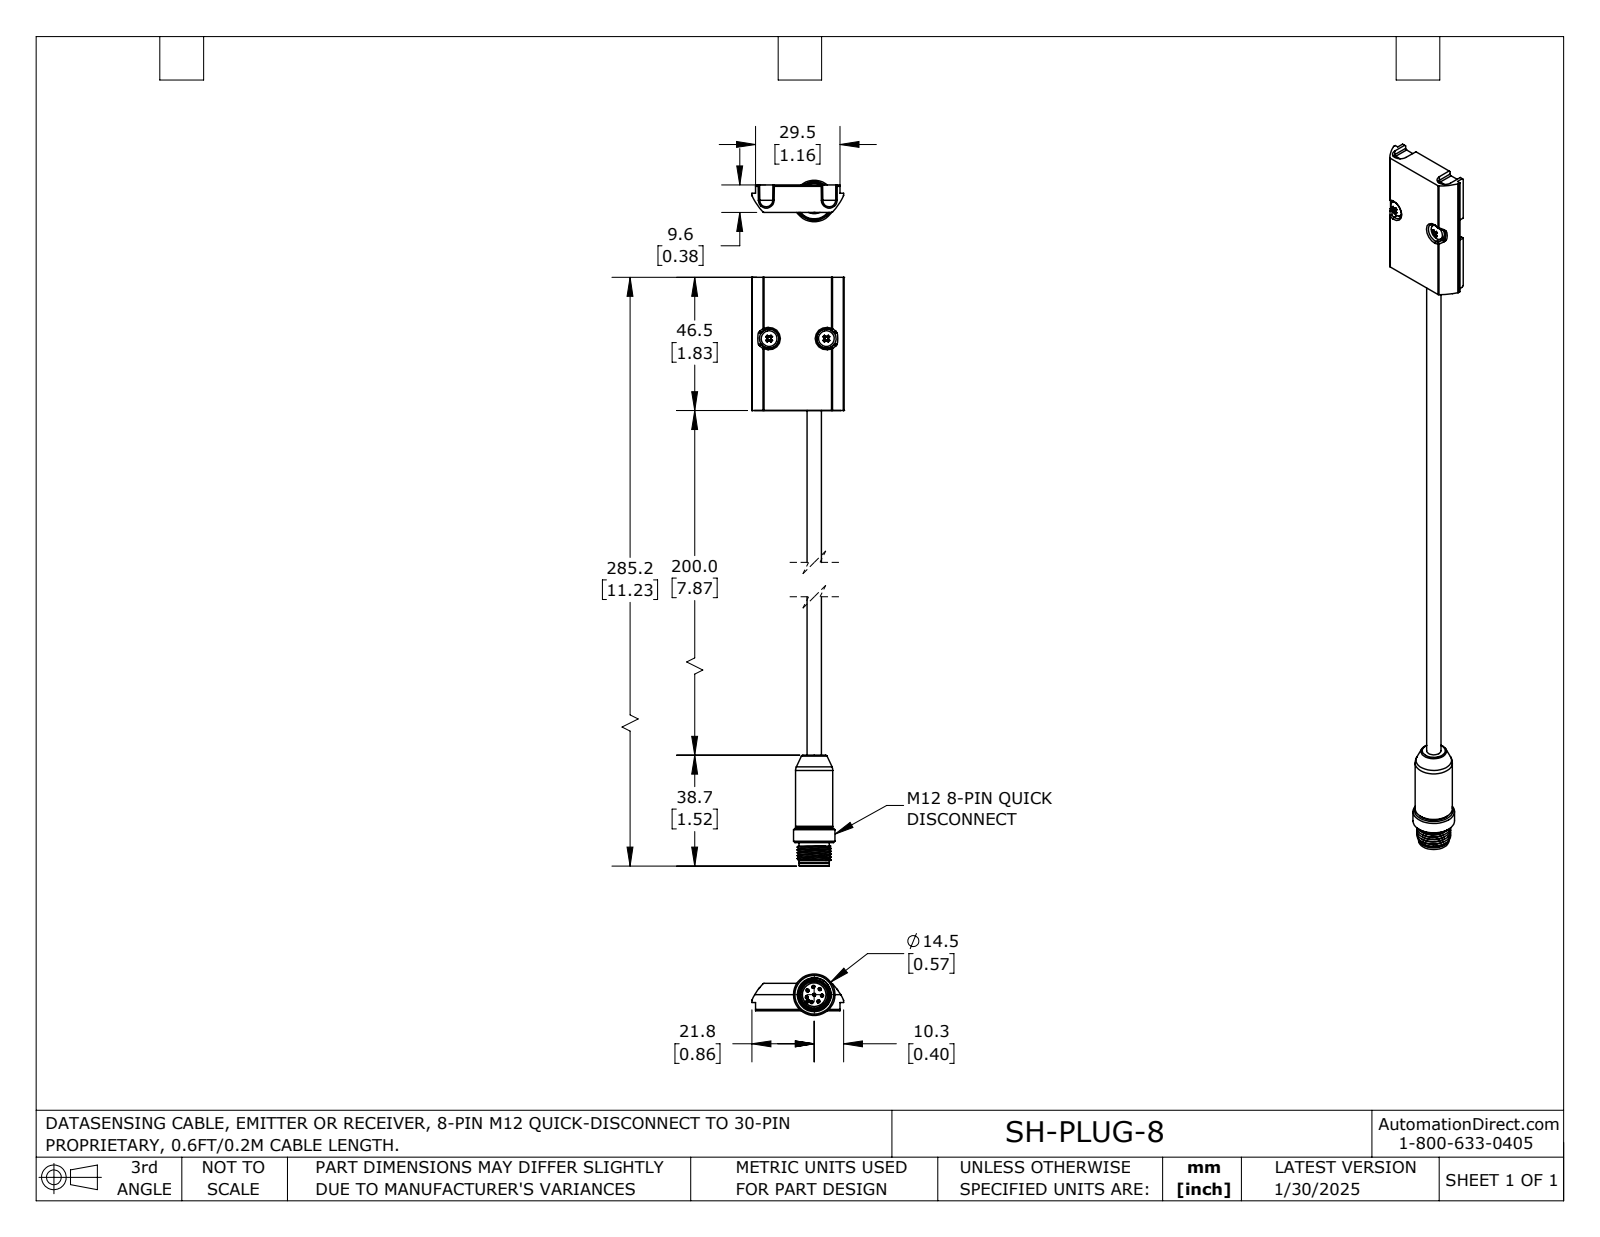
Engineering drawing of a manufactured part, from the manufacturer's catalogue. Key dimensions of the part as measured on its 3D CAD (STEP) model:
Part name (STEP PRODUCT): SH-PLUG-8
STEP written by: SolidWorks 2024 (AUTOMOTIVE_DESIGN)
Units: inches
Bodies: 1 solid, 427 faces (224 planar, 83 cylindrical, 120 other)
Overall size (bounding box): 11.228 × 1.26 × 0.571
Volume: 0.672 in³ · Surface area: 24.52 in²
Round holes (diameter × count): ⌀0.138 ×1, ⌀0.325 ×1, ⌀0.382 ×1, ⌀0.407 ×1, ⌀0.425 ×1
Round bosses / shafts (diameter × count): ⌀0.031 ×8, ⌀0.217 ×2, ⌀0.571 ×1, ⌀0.512 ×1, ⌀0.417 ×1, ⌀0.374 ×1, ⌀0.197 ×1
Partial cylindrical surfaces — rounded edges, fillets, slot ends (radius × count): R0.02 ×13, R0.008 ×10, R0.012 ×2, R0.108 ×2, R0.138 ×2, R0.197 ×2, R0.728 ×2, R0.748 ×2
Main face-to-face distances: 0.147, 0.059, 0.088, 0.056, 0.032, 0.091, 0.378, 0.322, 0.29, 0.231
